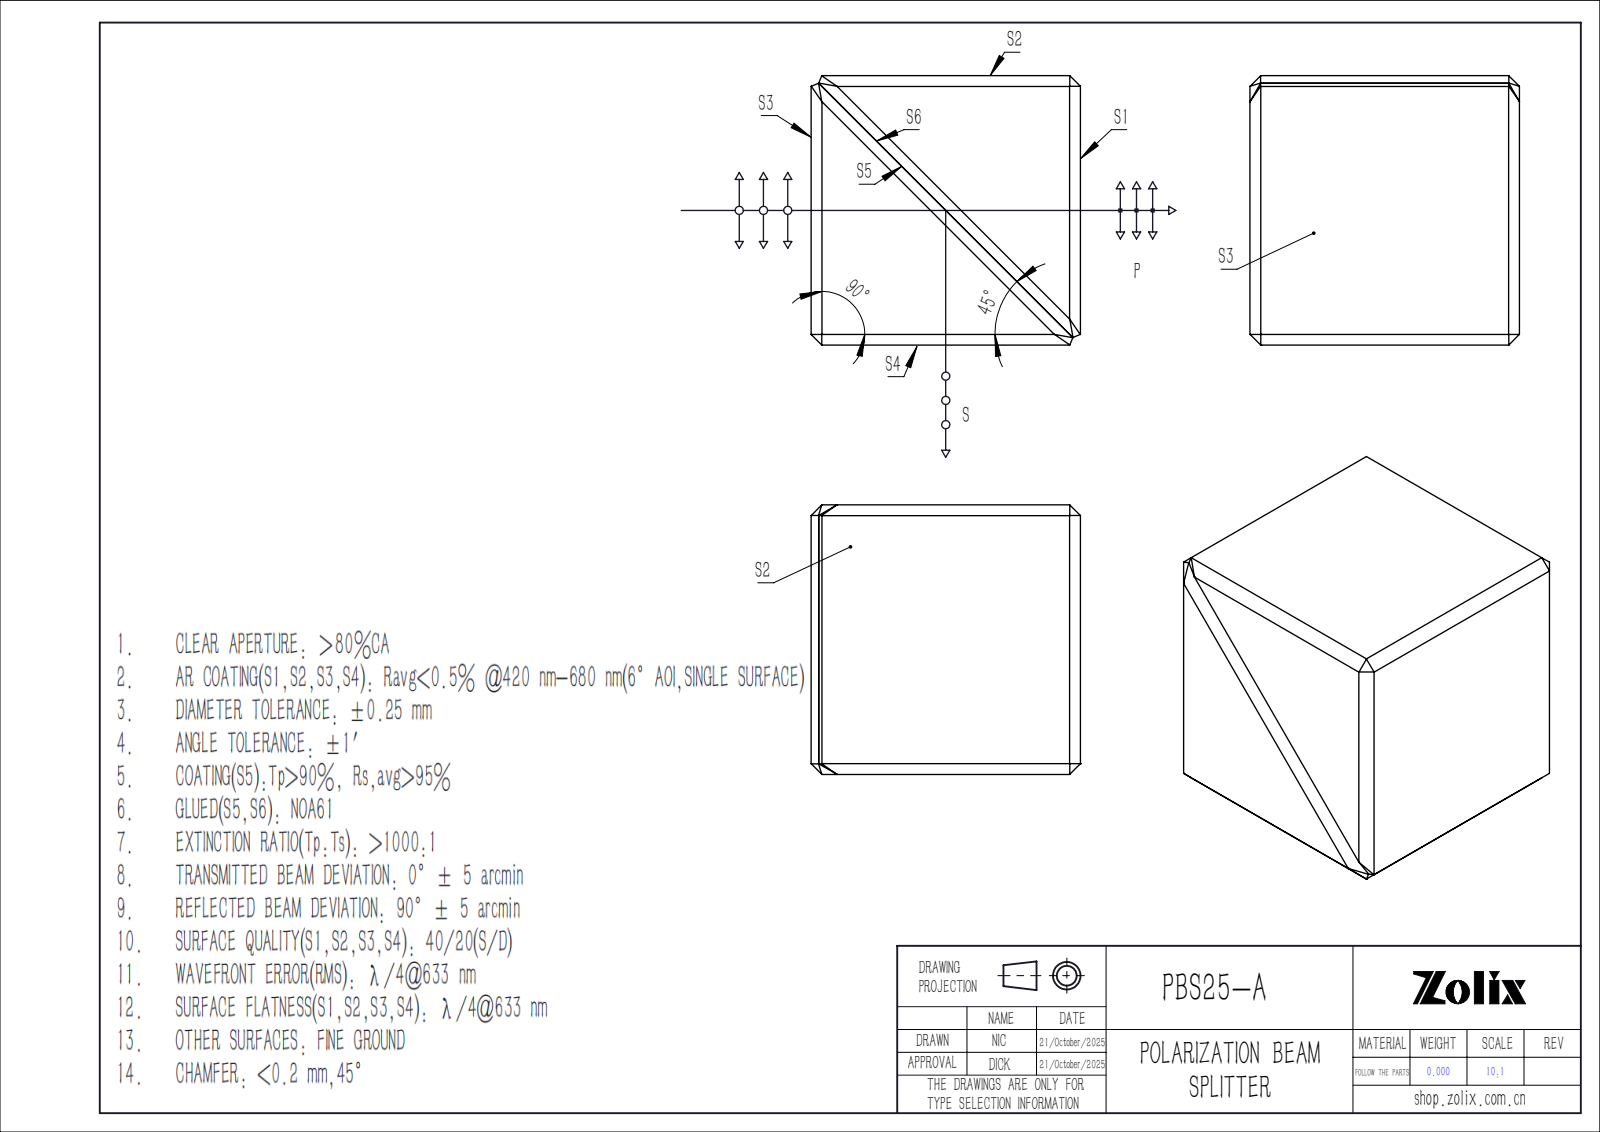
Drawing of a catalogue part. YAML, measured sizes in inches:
part_name: "PBS641; PBS641-1-2; PBS641-1-1"
step_written_by: "SolidWorks 2022 (CONFIG_CONTROL_DESIGN)"
units: inches
bodies: {solids: 2, faces: 43, planar: 41, cylindrical: 2, other: 0}
overall_size: [1, 1, 1]
volume: 0.999
surface_area: 8.717
round_holes:
  - {diameter: 0.02, count: 1}
face_to_face_distances: [1, 1.403, 0.696, 1.403, 1.293, 0.701, 0.702, 1.713, 1.501, 1.502]
